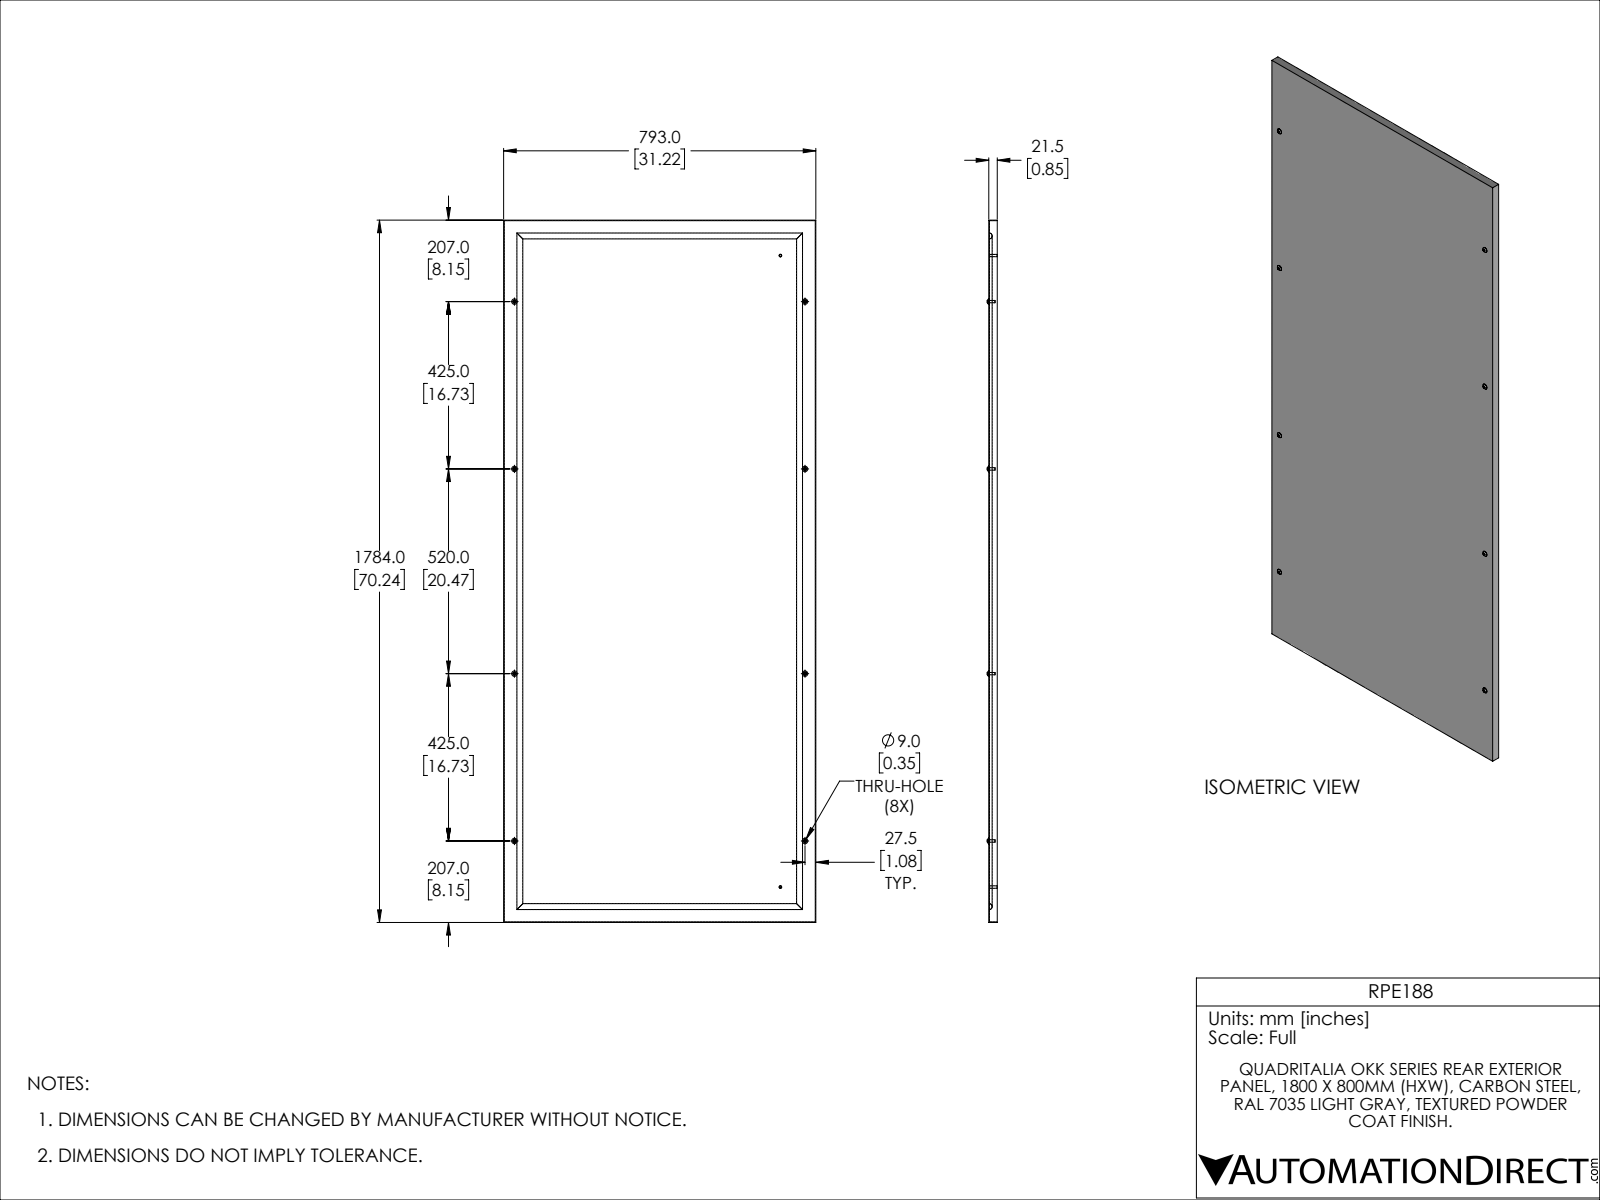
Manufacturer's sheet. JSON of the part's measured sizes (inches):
{"part_name": "RPE188", "step_written_by": "SolidWorks 2021 (CONFIG_CONTROL_DESIGN)", "units": "inches", "bodies": {"solids": 15, "faces": 311, "planar": 157, "cylindrical": 128, "other": 26}, "overall_size": [70.236, 31.22, 0.992], "volume_in3": 163.2, "surface_area_in2": 5009, "round_holes": [[0.354, 8]], "round_bosses_or_shafts": [[0.236, 10], [0.551, 8], [0.276, 2]], "partial_cylinders_radius": [[0.02, 96], [0.296, 4]], "face_to_face_distances": [0.059, 31.161, 31.22, 31.102, 70.177, 70.236, 70.118, 0.846, 0.787, 27.64], "hole_center_spacings": [16.732, 29.055, 33.529, 37.205, 47.206, 20.472, 35.543, 53.937]}
